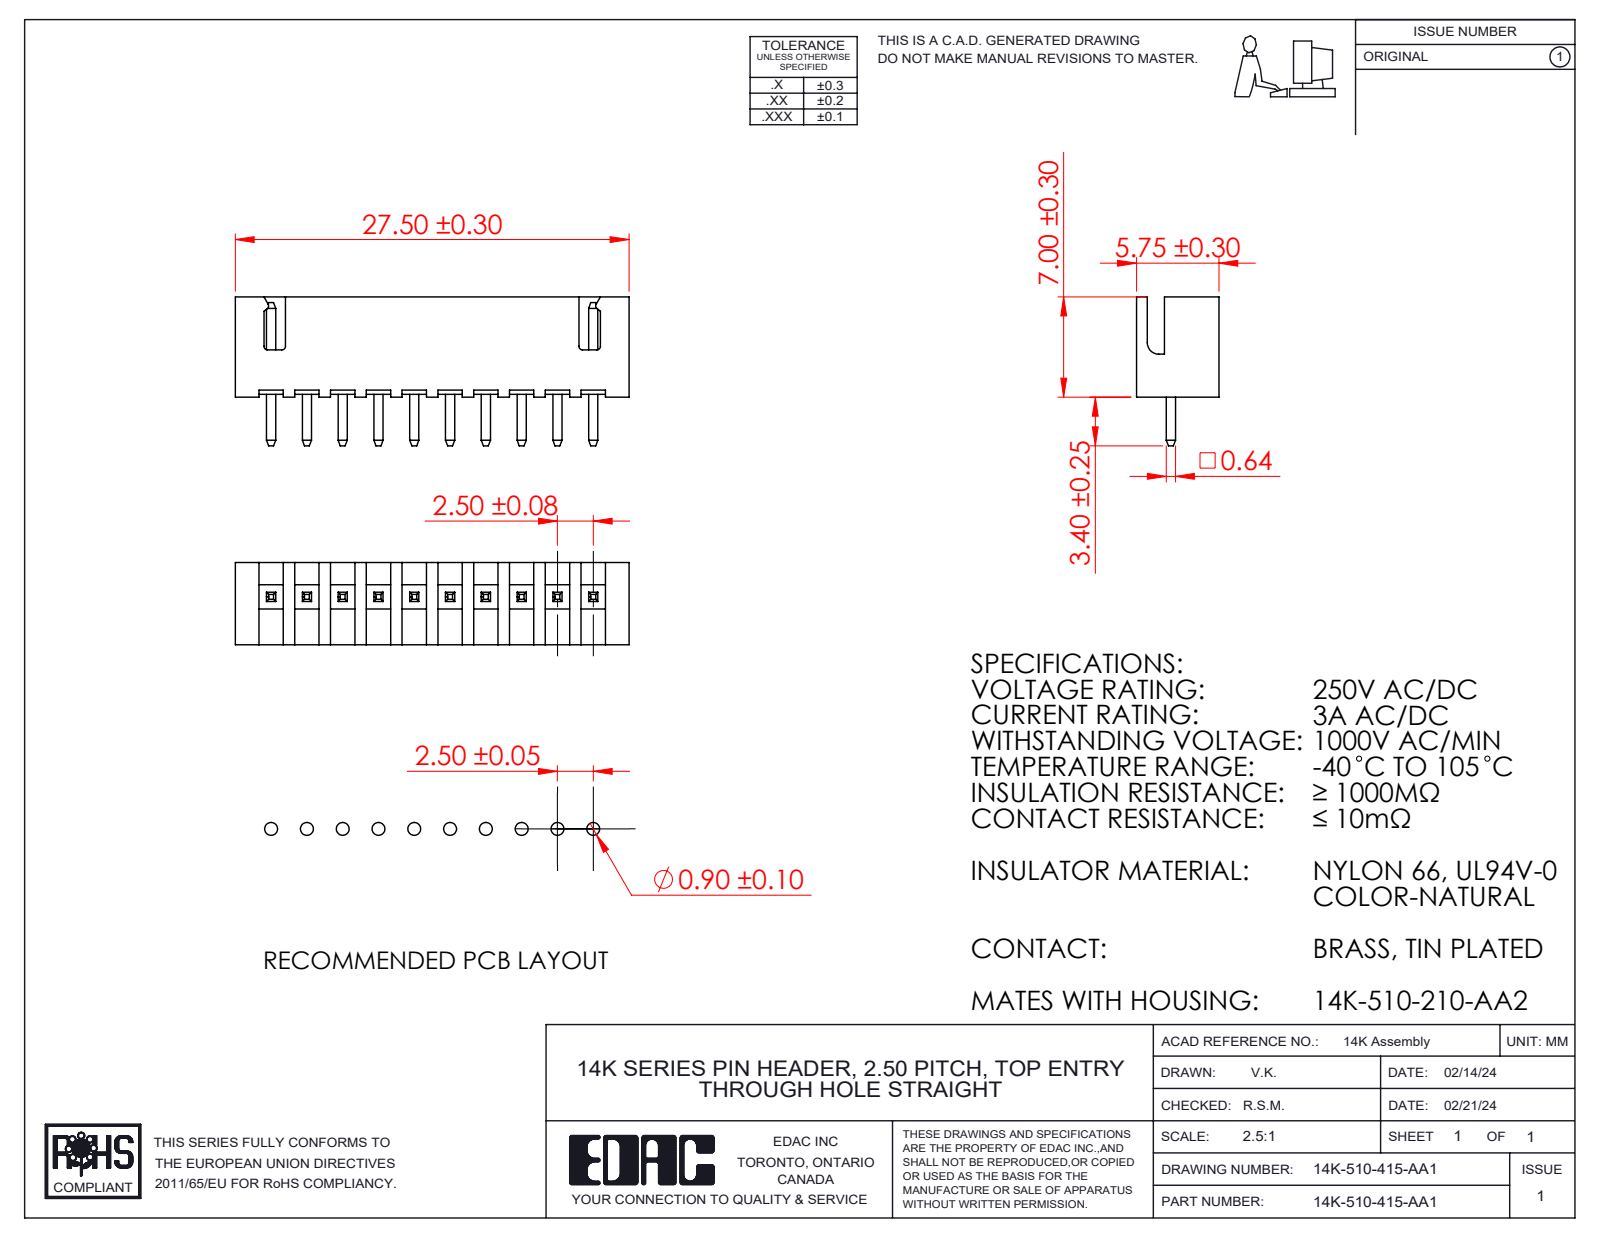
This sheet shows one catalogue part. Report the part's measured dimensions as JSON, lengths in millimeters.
{"part_name": "14K Series Pin_15; 14K-510-415-AA1; 14K Series Pin Header Insulator_510", "step_written_by": "SolidWorks 2023 (CONFIG_CONTROL_DESIGN)", "units": "millimeters", "bodies": {"solids": 11, "faces": 300, "planar": 291, "cylindrical": 9, "other": 0}, "overall_size": [27.5, 10.4, 5.75], "volume_mm3": 512, "surface_area_mm2": 1397, "partial_cylinders_radius": [[0.25, 6], [0.8, 1]], "face_to_face_distances": [5, 0.76, 5.76, 4.24, 0.64, 2.5, 7.5, 3.04, 2.28, 1.96]}
